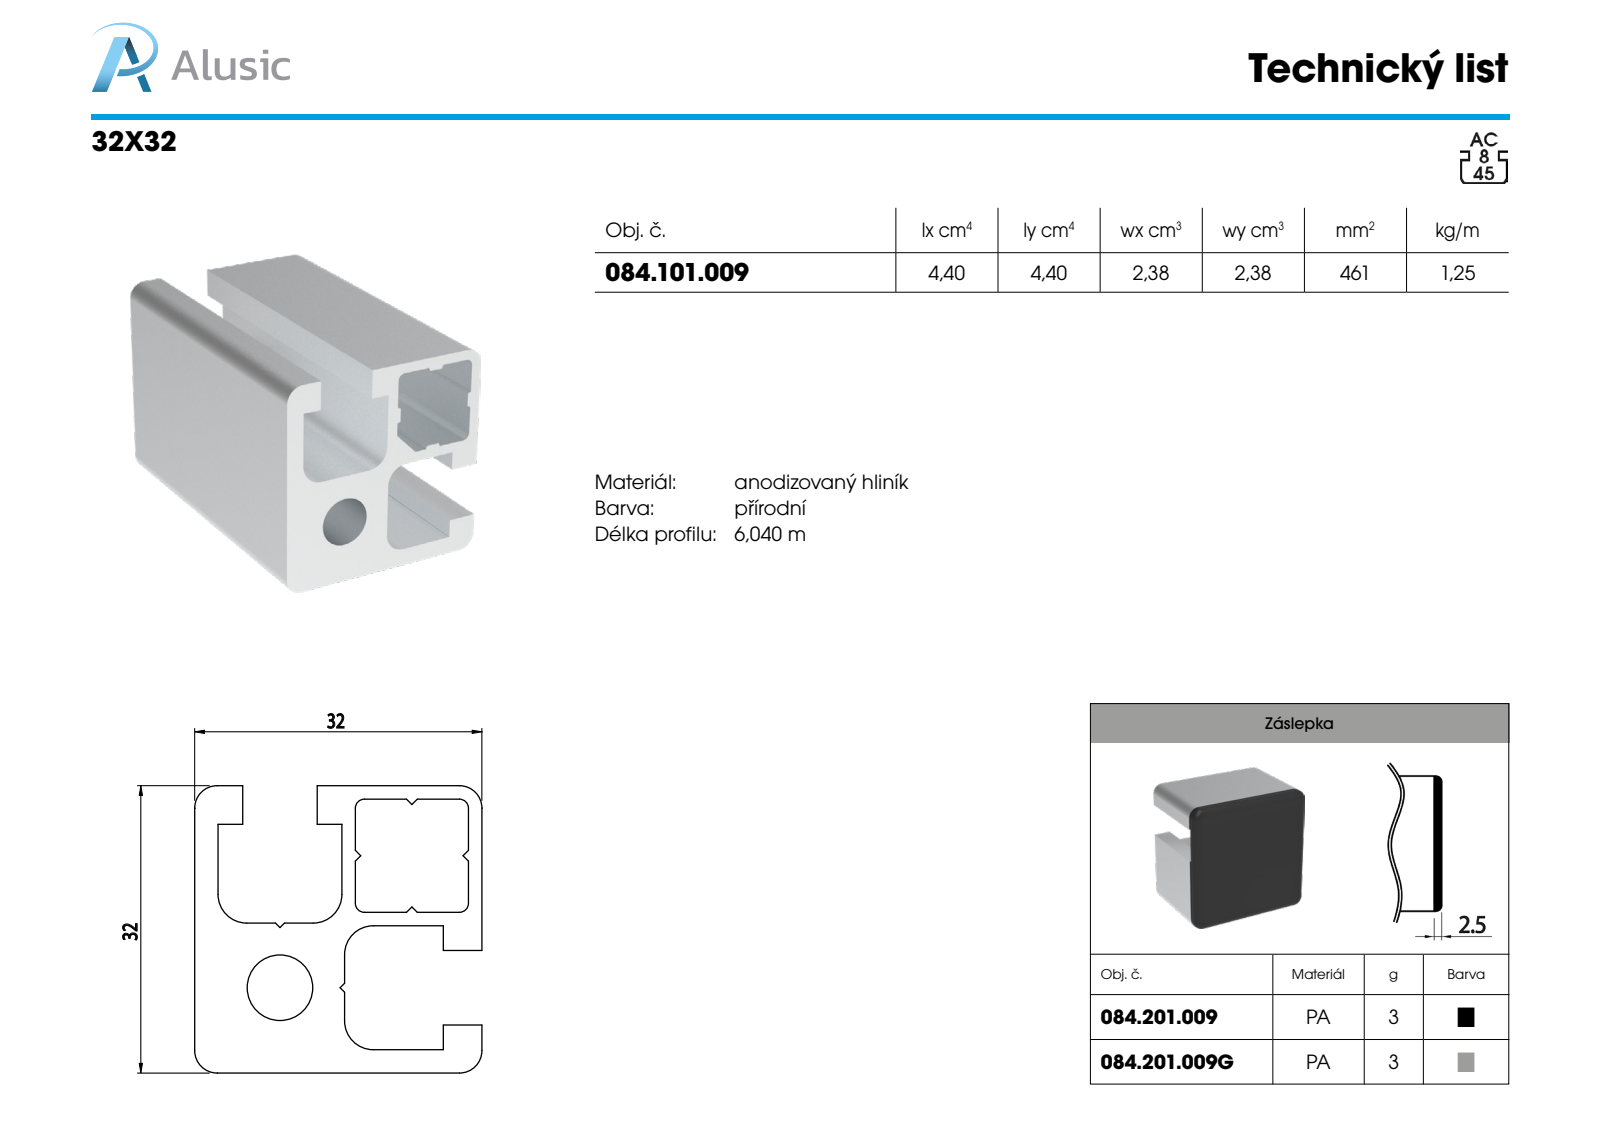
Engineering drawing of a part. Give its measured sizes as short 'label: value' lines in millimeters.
name: 084.101.009
written by: SolidWorks 2018 (AUTOMOTIVE_DESIGN)
unit: mm
bodies: 1 solid, 56 faces (43 planar, 13 cylindrical, 0 other)
size: 100 × 32 × 32
volume: 46 219 mm³; area: 28 365 mm²
holes: 1× ⌀7.3
rounds: 4× R2.5, 4× R3, 3× R1
face distances: 14.1, 32, 13.8, 1.5, 15.3, 2.75, 11.05, 30.5, 2.6, 27.9
